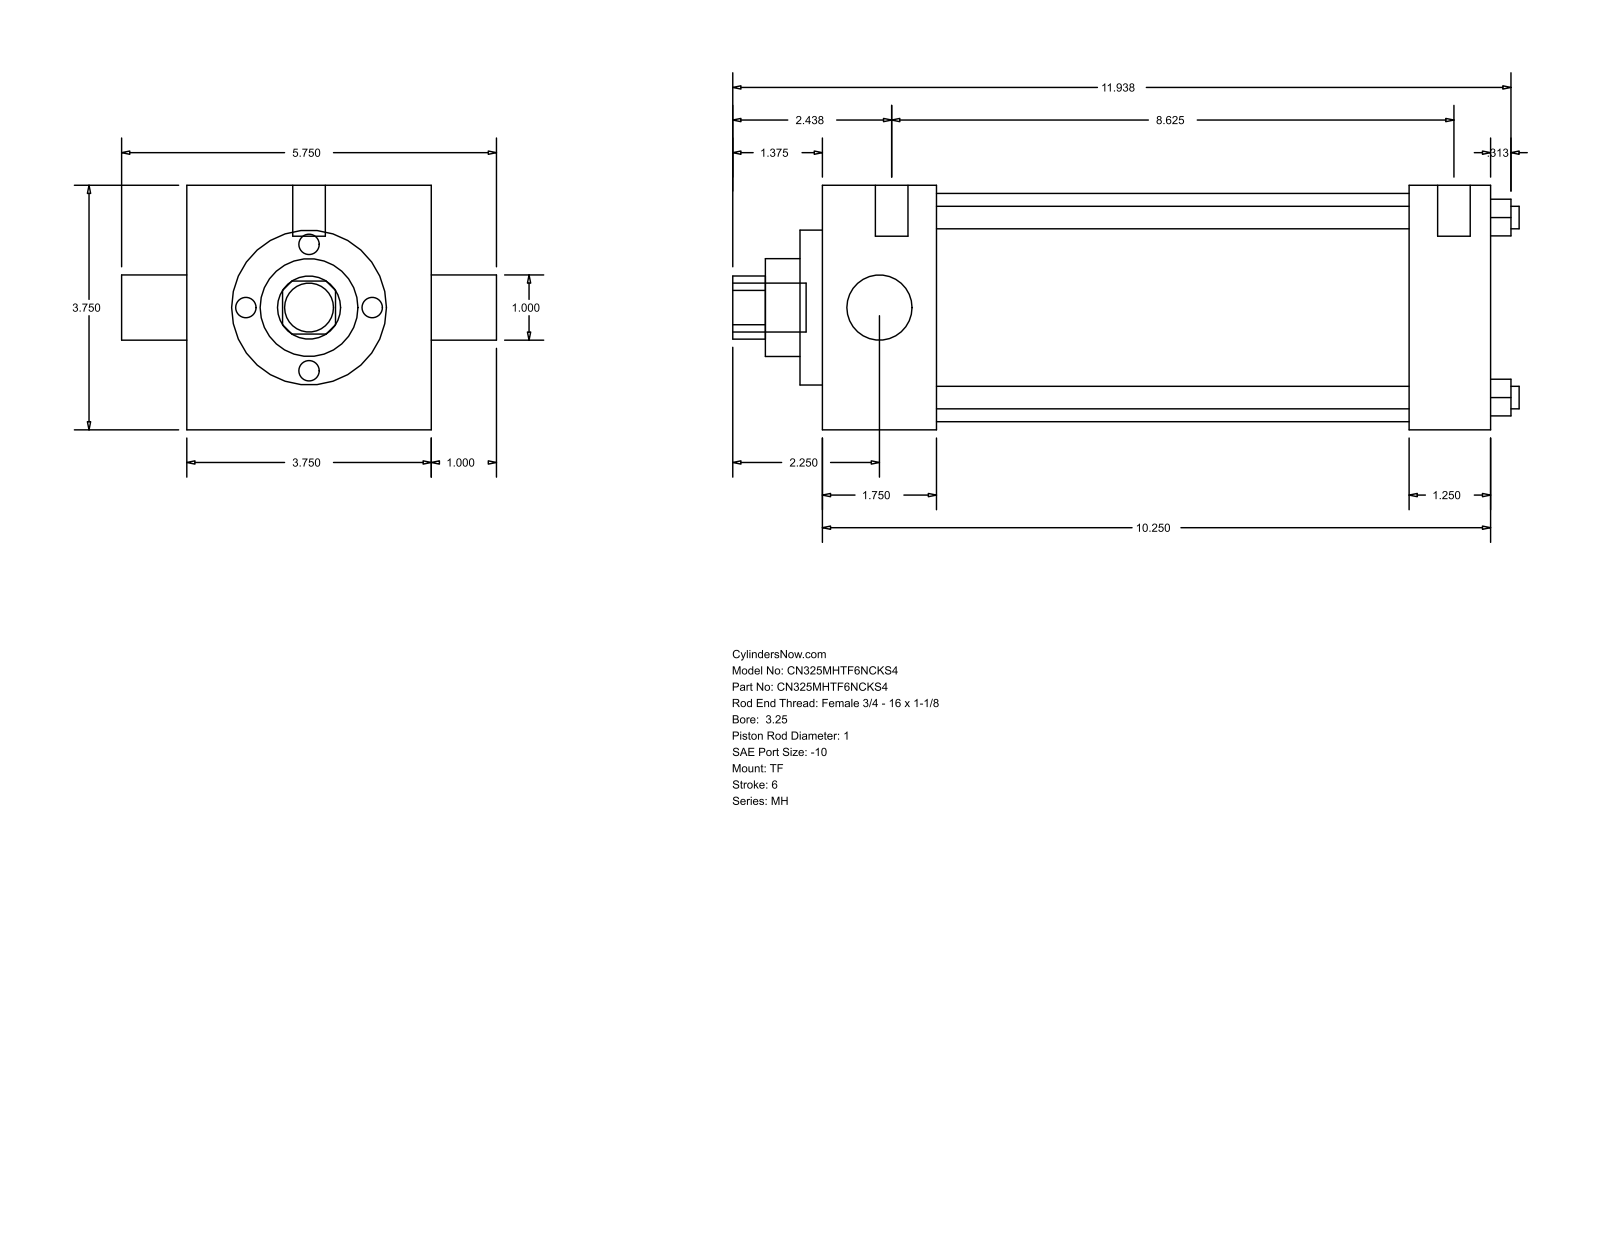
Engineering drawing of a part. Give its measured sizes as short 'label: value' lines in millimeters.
name: MH_TF__0325_1
written by: GSSL Pune (CONFIG_CONTROL_DESIGN)
unit: mm
bodies: 0 solids, 86 faces (61 planar, 25 cylindrical, 0 other)
size: 306.39 × 146.05 × 95.25
holes: 4× ⌀8.76, 2× ⌀25.4, 1× ⌀38.1, 1× ⌀60.33, 1× ⌀88.9
bosses: 3× ⌀5.56, 2× ⌀12.7, 1× ⌀19.05
rounds: 1× R12.29
face distances: 95.24, 260.35, 44.46, 228.6, 184.14, 215.89, 31.75, 8.73, 53.19, 237.33
hole spacings: 49.57, 70.1, 99.14
